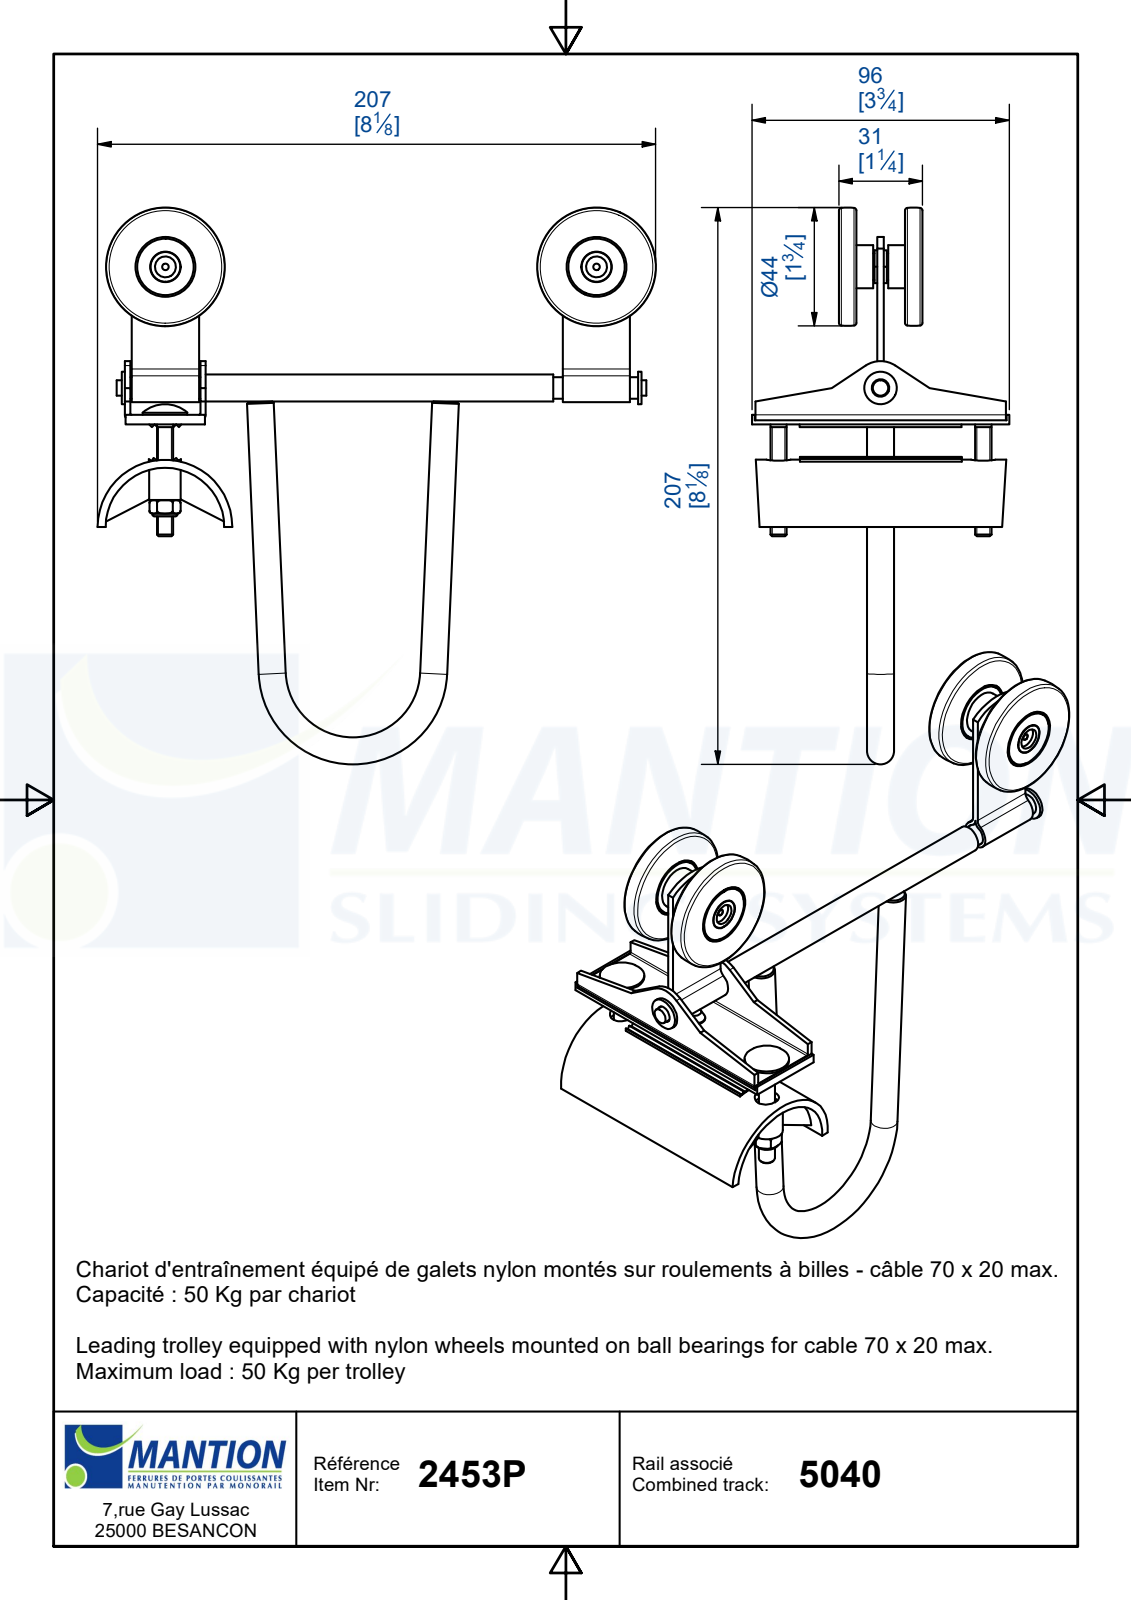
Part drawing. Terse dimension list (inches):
name: 2453P; 15735; 17242; 15292 (+8 more)
written by: Autodesk Inventor 2013 (AUTOMOTIVE_DESIGN)
unit: in
bodies: 19 solids, 377 faces (233 planar, 94 cylindrical, 50 other)
size: 8.154 × 8.141 × 3.76
volume: 8.106 in³; area: 129.6 in²
holes: 2× ⌀0.093, 2× ⌀0.194, 2× ⌀0.256, 2× ⌀0.307, 2× ⌀0.354, 2× ⌀0.396, 2× ⌀0.873, 1× ⌀0.244, 1× ⌀0.252, 1× ⌀0.315, 1× ⌀0.319
bosses: 3× ⌀0.472, 3× ⌀0.394, 3× ⌀0.236, 2× ⌀0.82, 2× ⌀0.652, 2× ⌀0.63, 2× ⌀0.445, 2× ⌀0.39
rounds: 4× R0.118, 2× R0.02, 2× R0.079, 2× R0.787, 1× R0.394, 1× R0.866, 1× R0.984
face distances: 0.256, 0.965, 0.079, 1.22, 0.059, 0.709, 0.138, 0.561, 0.305, 0.404
hole spacings: 1.491, 1.501, 2.992, 6.299
